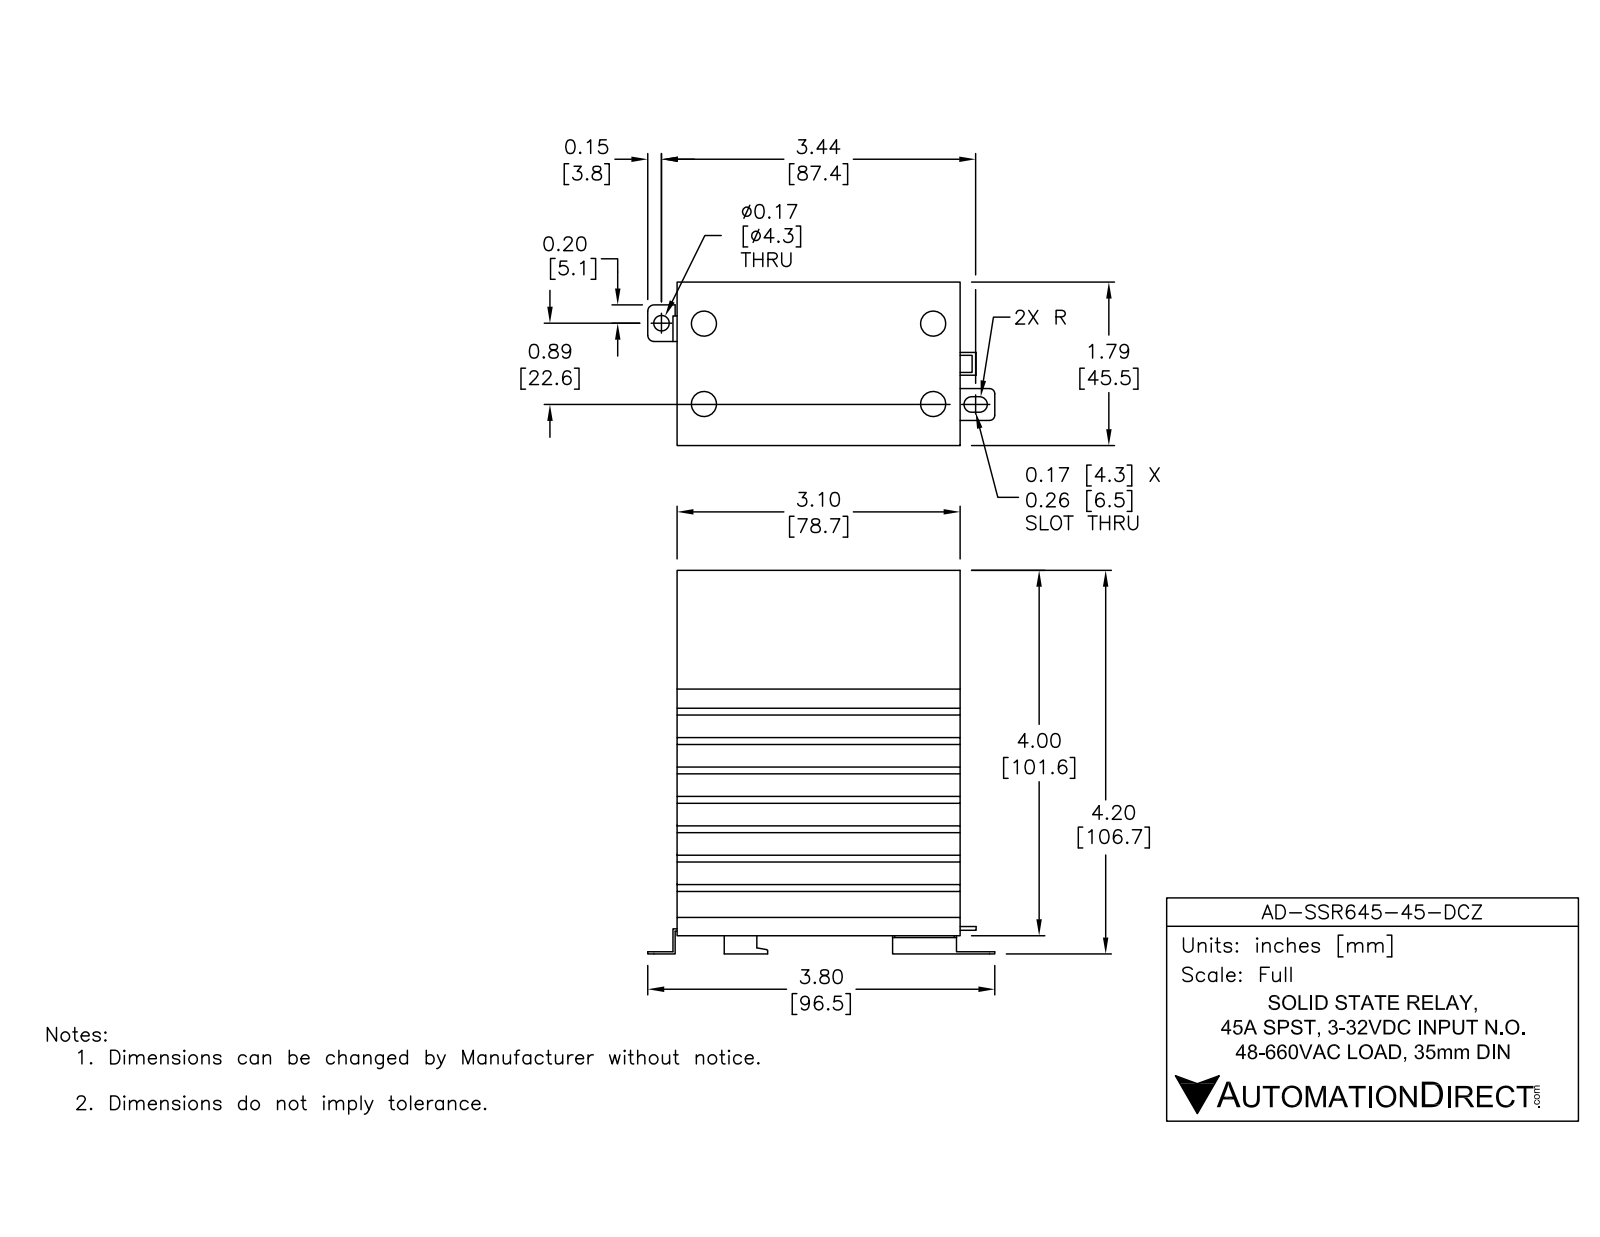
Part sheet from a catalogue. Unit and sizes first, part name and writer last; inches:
Units: inches
Overall size (bounding box): 4.2 × 3.8 × 1.79
Round holes (diameter × count): ⌀0.275 ×2, ⌀0.275 ×2, ⌀0.17 ×1
Partial cylindrical surfaces — rounded edges, fillets, slot ends (radius × count): R0.05 ×2, R0.058 ×2, R0.067 ×2, R0.085 ×2, R0.015 ×1
Main face-to-face distances: 0.644, 0.322, 0.966, 0.397, 0.322, 0.247, 1.609, 0.075, 0.569, 0.075
Hole centre spacings: 0.88, 2.51, 2.66, 0.465, 1, 2.975, 3.104
Volume: 12.46 in³ · Surface area: 125.1 in²
Bodies: 1 solid, 171 faces (151 planar, 20 cylindrical, 0 other)
Part name (STEP PRODUCT): AD-SSR645-45-DCZ
STEP written by: SolidWorks 2014 (AUTOMOTIVE_DESIGN)
